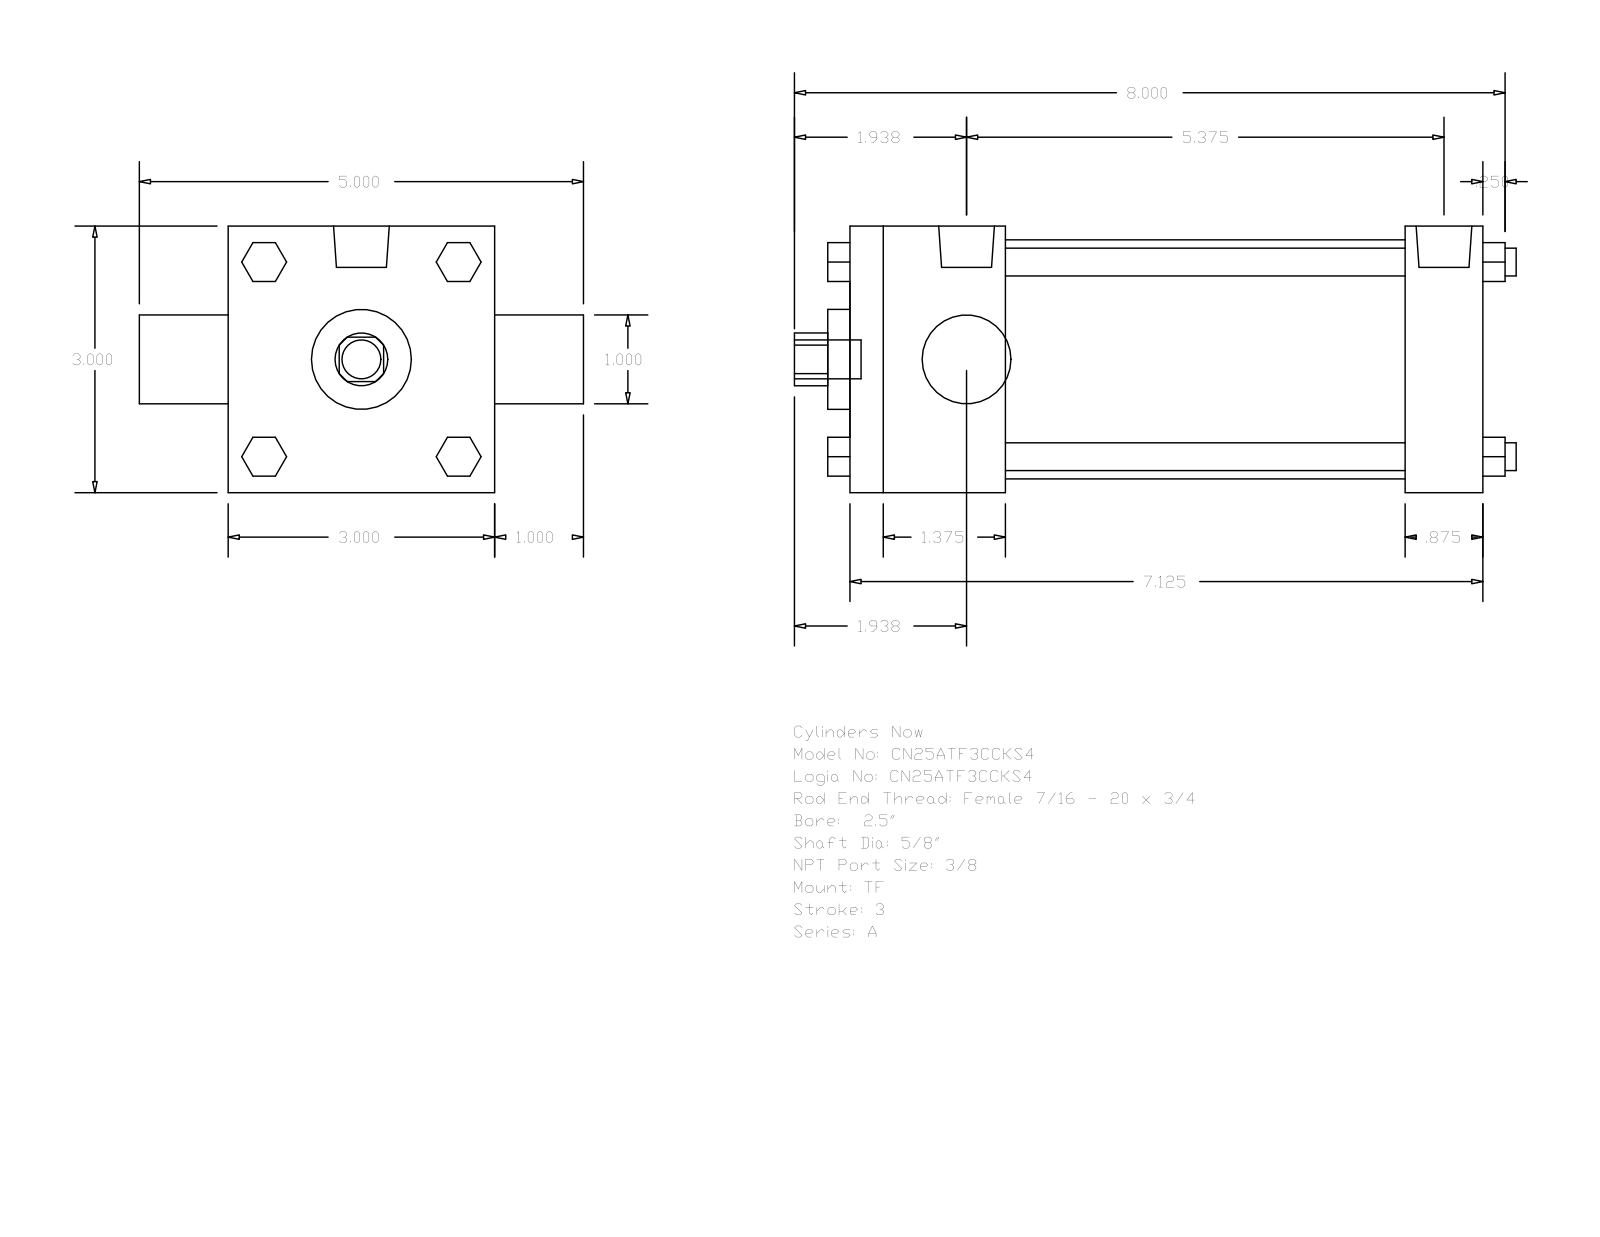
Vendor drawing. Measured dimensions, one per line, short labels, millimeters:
name: A_TF__0250_0.625
written by: GSSL Pune (CONFIG_CONTROL_DESIGN)
unit: mm
bodies: 0 solids, 120 faces (92 planar, 28 cylindrical, 0 other)
size: 206.38 × 127 × 76.2
holes: 1× ⌀15.88, 1× ⌀25.4, 1× ⌀28.57, 1× ⌀68.33
bosses: 4× ⌀7.94, 3× ⌀5.56, 2× ⌀15.93, 1× ⌀11.11
rounds: 1× R7.54
face distances: 76.2, 180.97, 44.45, 158.74, 114.29, 136.52, 22.23, 25.4, 101.6, 6.35
